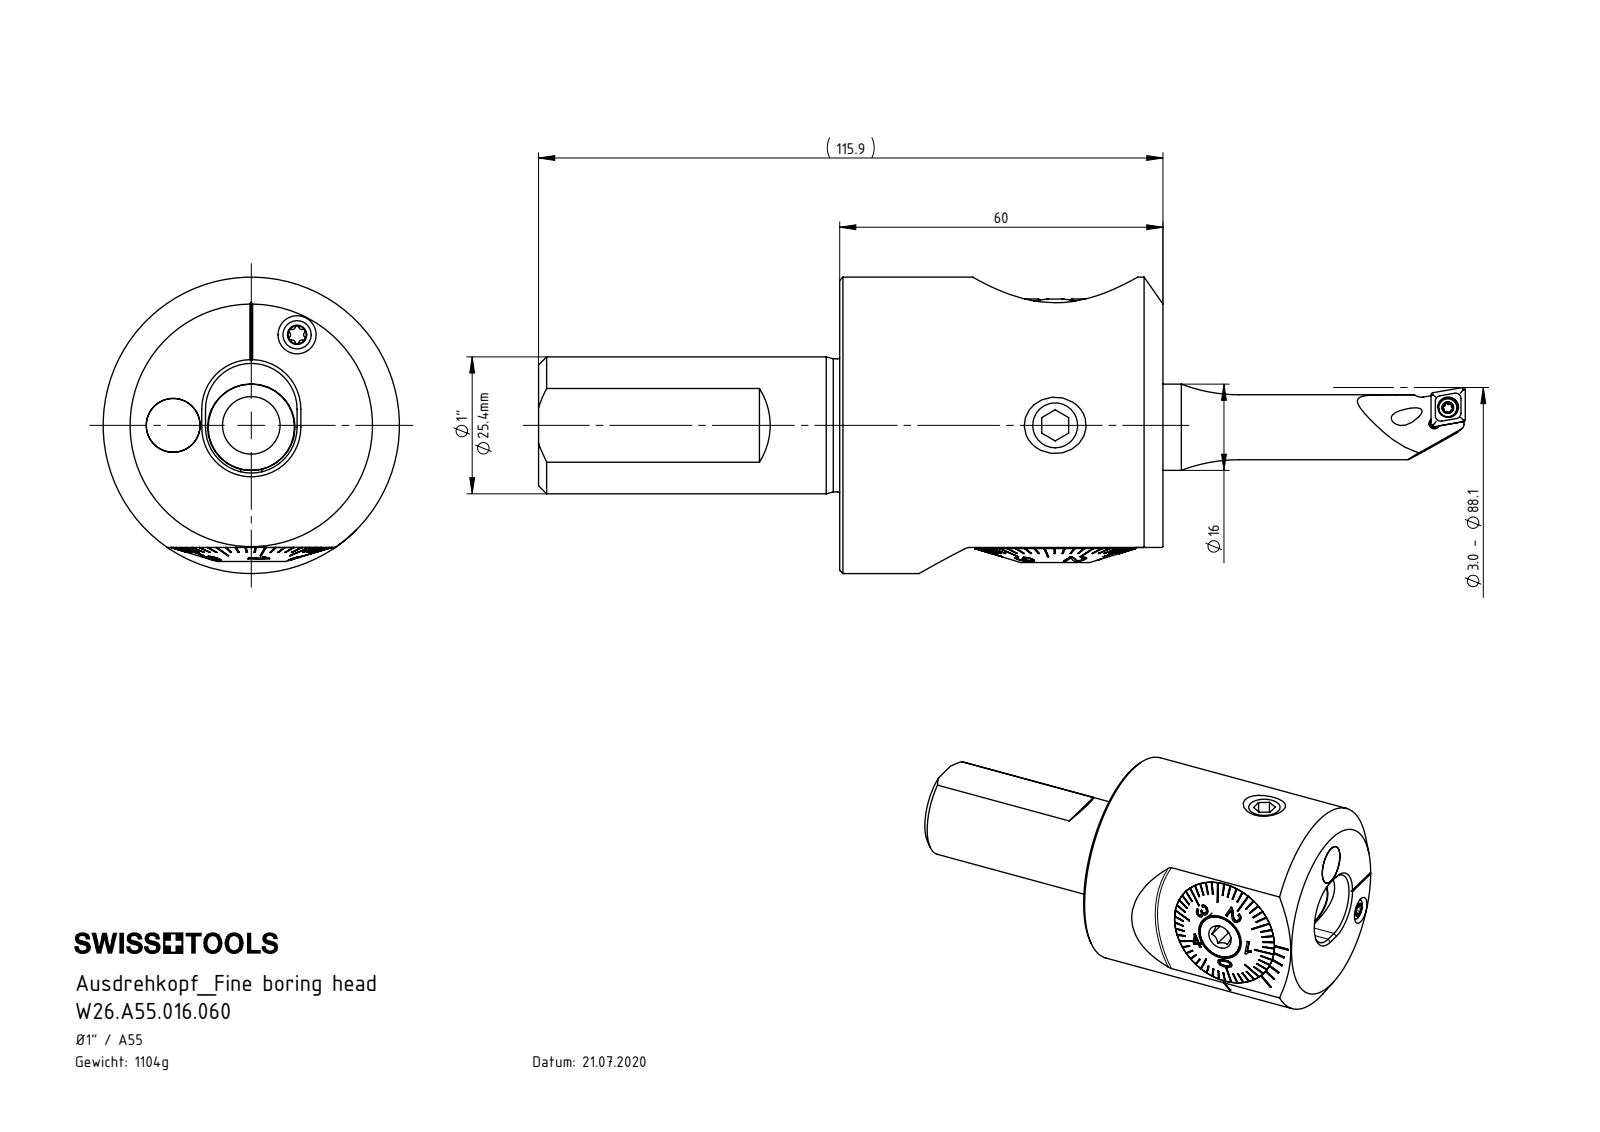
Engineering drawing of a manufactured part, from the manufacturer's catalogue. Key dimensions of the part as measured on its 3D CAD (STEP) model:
Part name (STEP PRODUCT): WCB-ER2.001.009_A; W26-A55.AA3.060_A_Fertigbearbeitung; ISO 4026 - M10 x 8; ISO 4026 - M10 x 16_PreviewCfg (+8 more)
STEP written by: SolidWorks 2017 (AUTOMOTIVE_DESIGN)
Units: millimetres
Bodies: 14 solids, 570 faces (315 planar, 79 cylindrical, 176 other)
Overall size (bounding box): 115.9 × 55 × 55
Volume: 138 584 mm³ · Surface area: 42 545 mm²
Round holes (diameter × count): ⌀8.5 ×3, ⌀1.6 ×1, ⌀3.3 ×1, ⌀4.2 ×1, ⌀8 ×1, ⌀10 ×1, ⌀10.7 ×1, ⌀11.4 ×1, ⌀12.4 ×1, ⌀13.5 ×1, ⌀14 ×1, ⌀14.2 ×1
Round bosses / shafts (diameter × count): ⌀10 ×3, ⌀55 ×1, ⌀30 ×1, ⌀29.98 ×1, ⌀29.9 ×1, ⌀25.4 ×1, ⌀25 ×1, ⌀24.7 ×1
Partial cylindrical surfaces — rounded edges, fillets, slot ends (radius × count): R0.34 ×6, R0.59 ×6, R1.4 ×4, R1.9 ×4, R3.2 ×3, R2 ×2, R8.5 ×2, R1 ×1
Main face-to-face distances: 60, 5.3, 2.8, 2.5, 6.5, 3.7, 1.2, 5, 5.2, 6.4
Hole centre spacings: 14.5, 7.25, 0.35, 18.83, 19.14, 28.48
